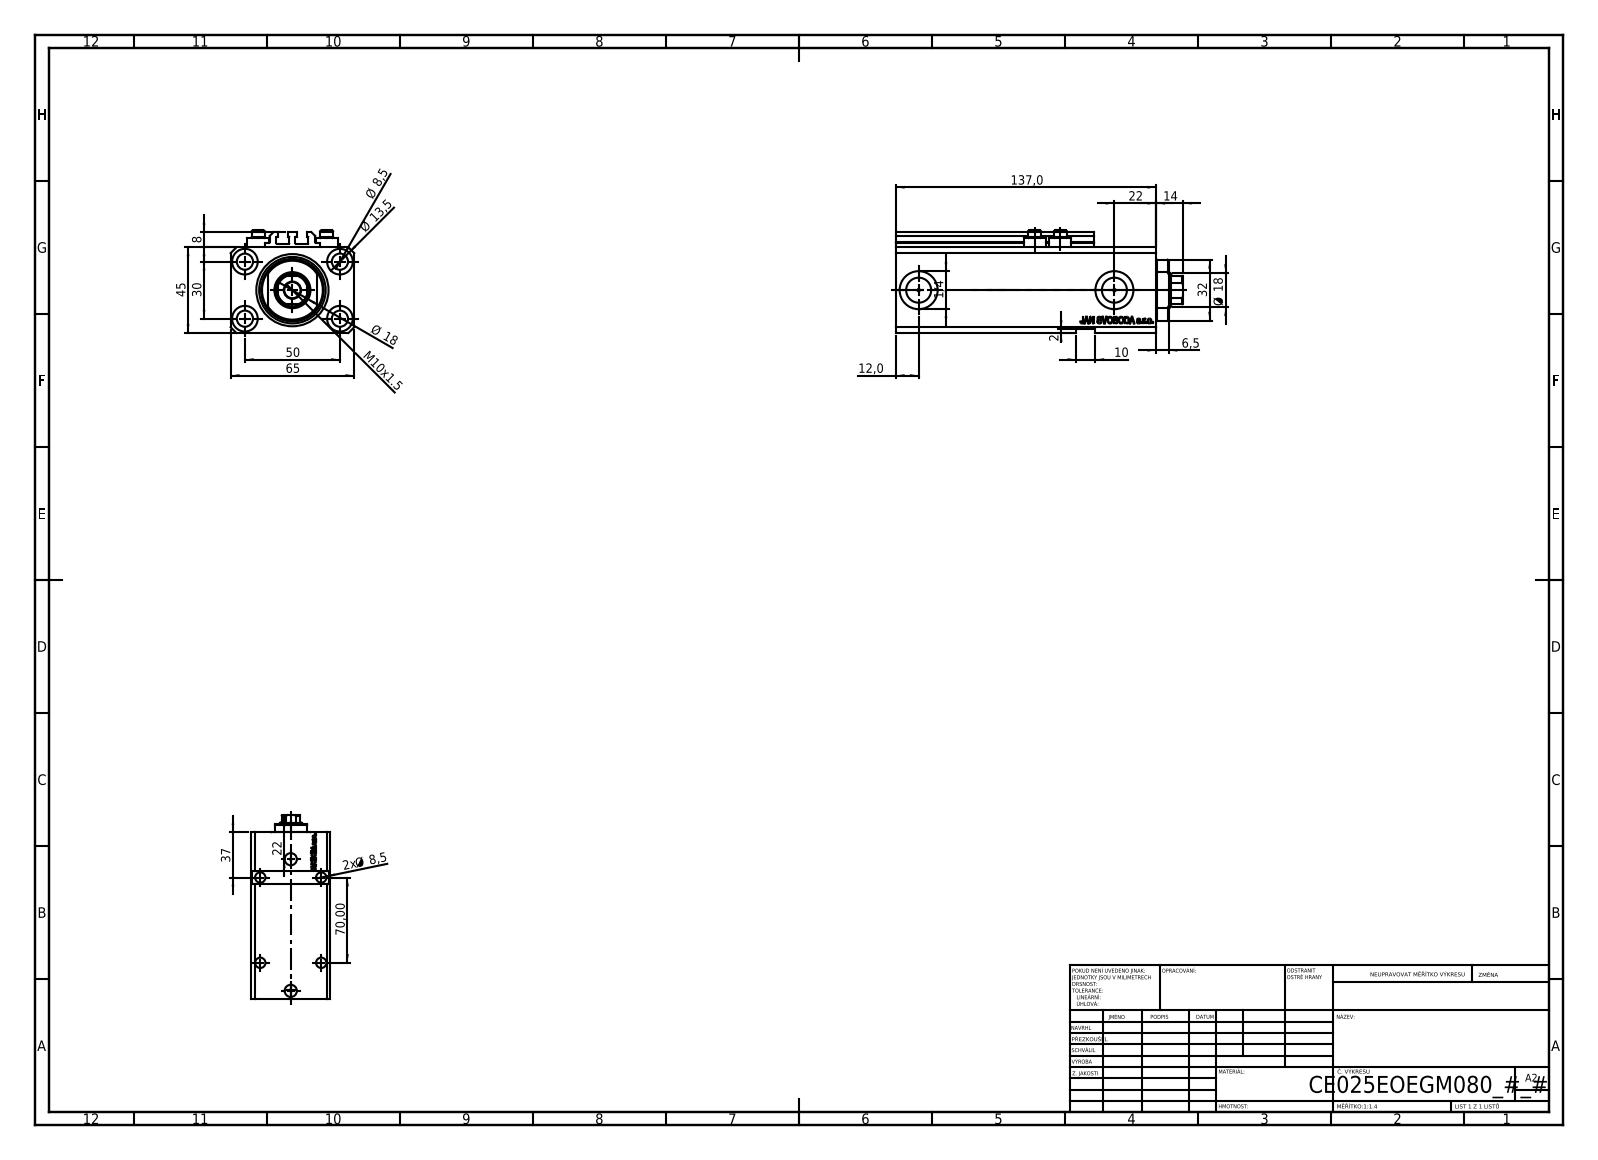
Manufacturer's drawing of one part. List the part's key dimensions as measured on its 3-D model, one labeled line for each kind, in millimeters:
Part name (STEP PRODUCT): V250CE_VC_E; ALLEN BOLT V250CE; V250CE_E_Body; V250CE_C_VCP
STEP written by: SolidWorks 2019 (CONFIG_CONTROL_DESIGN)
Units: millimetres
Bodies: 8 solids, 1087 faces (511 planar, 146 cylindrical, 430 other)
Overall size (bounding box): 151 × 65 × 54
Volume: 350 493 mm³ · Surface area: 93 546 mm²
Round holes (diameter × count): ⌀8.5 ×9, ⌀1.25 ×4, ⌀4 ×4, ⌀13.5 ×4, ⌀10 ×2, ⌀13.16 ×2, ⌀20 ×2, ⌀18 ×1, ⌀25 ×1, ⌀38 ×1
Round bosses / shafts (diameter × count): ⌀11.6 ×4, ⌀7 ×4
Partial cylindrical surfaces — rounded edges, fillets, slot ends (radius × count): R0.2 ×10, R8.5 ×1, R16 ×1
Main face-to-face distances: 45, 65, 47, 2, 123, 2.5, 14, 10, 137, 20.5
Hole centre spacings: 29.15, 50, 13.6, 15.12, 27.89, 30, 33.61, 33.62
